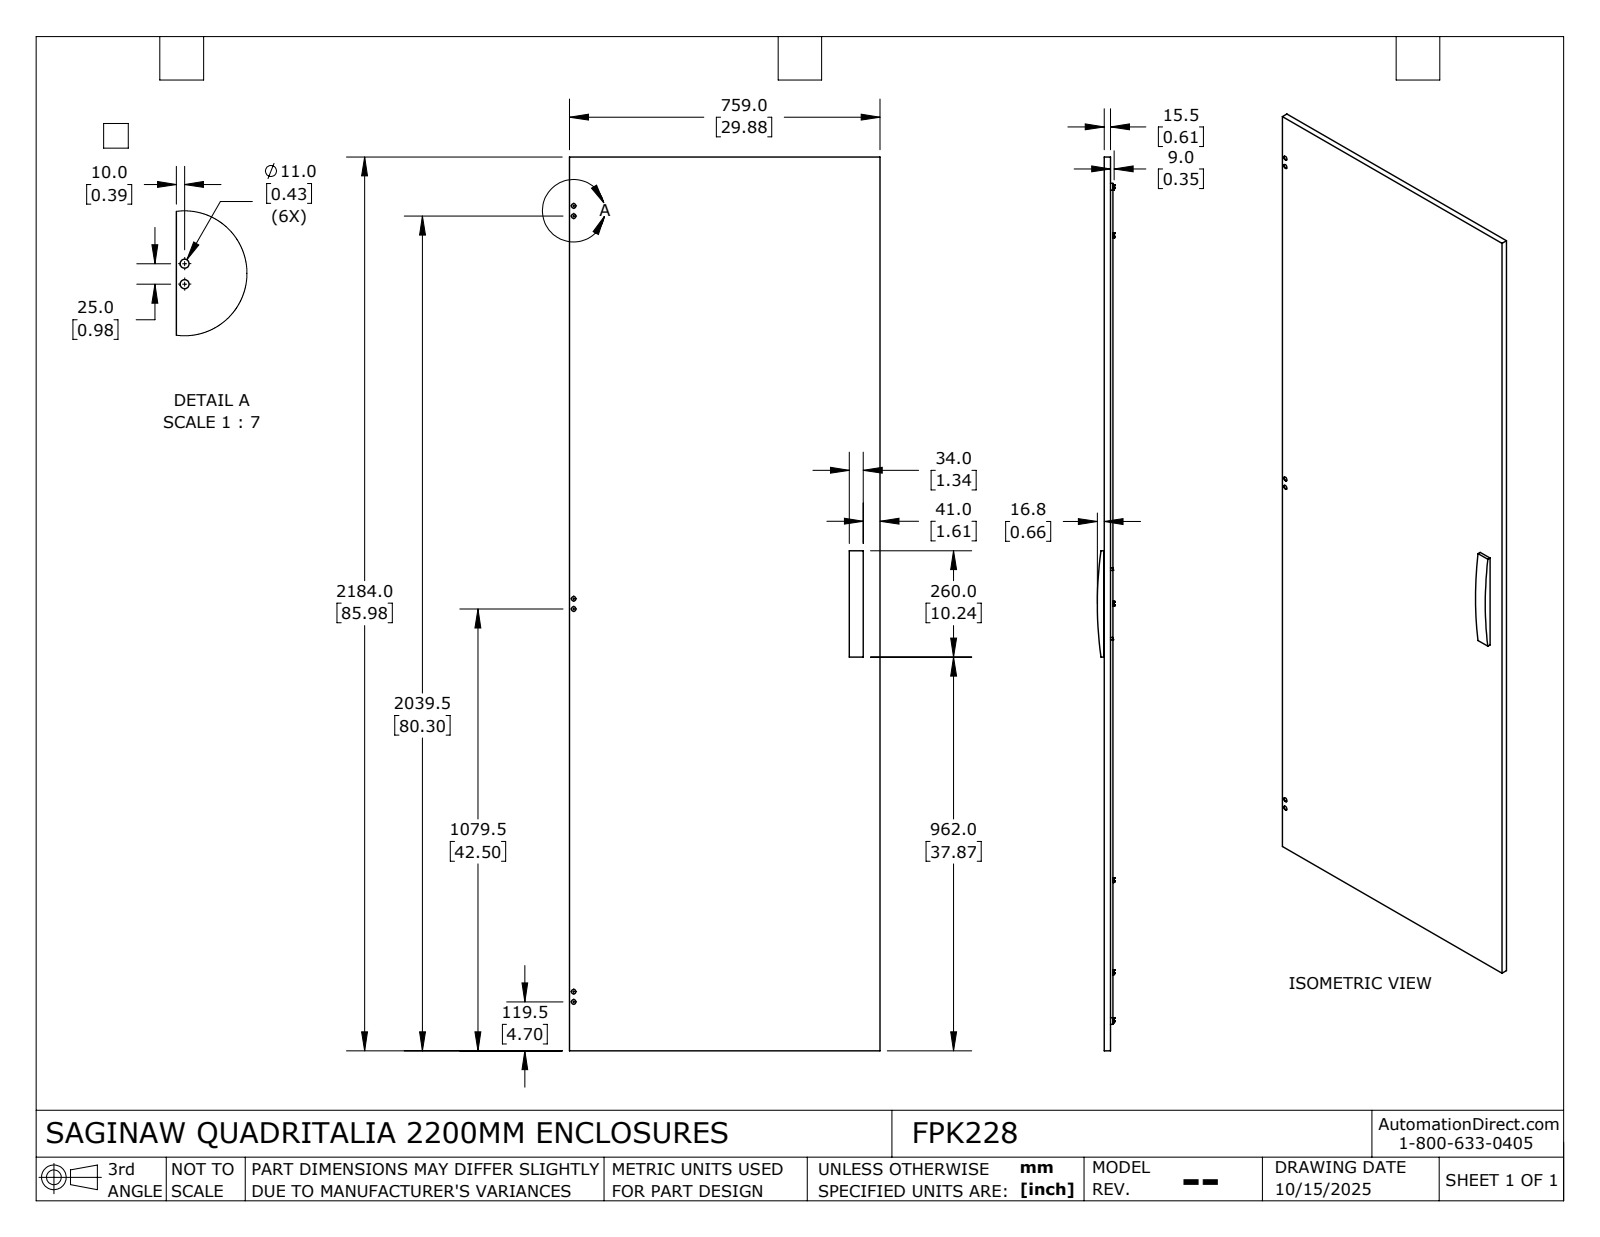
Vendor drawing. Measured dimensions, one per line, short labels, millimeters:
name: FPK228
written by: SolidWorks 2024 (AUTOMOTIVE_DESIGN)
unit: mm
bodies: 2 solids, 702 faces (331 planar, 267 cylindrical, 104 other)
size: 2184 × 759 × 41.32
volume: 4 931 000 mm³; area: 3 876 000 mm²
holes: 168× ⌀4.25, 17× ⌀9, 7× ⌀4.92, 6× ⌀11, 2× ⌀2.5, 1× ⌀4.92
bosses: 7× ⌀7, 7× ⌀6, 3× ⌀7.2
rounds: 8× R1, 8× R5.77, 4× R7.52, 1× R962.86
face distances: 1.5, 20, 21.5, 560, 18.5, 757.5, 580, 540, 83, 75
hole spacings: 25, 50, 75, 100, 125, 150, 175, 200
